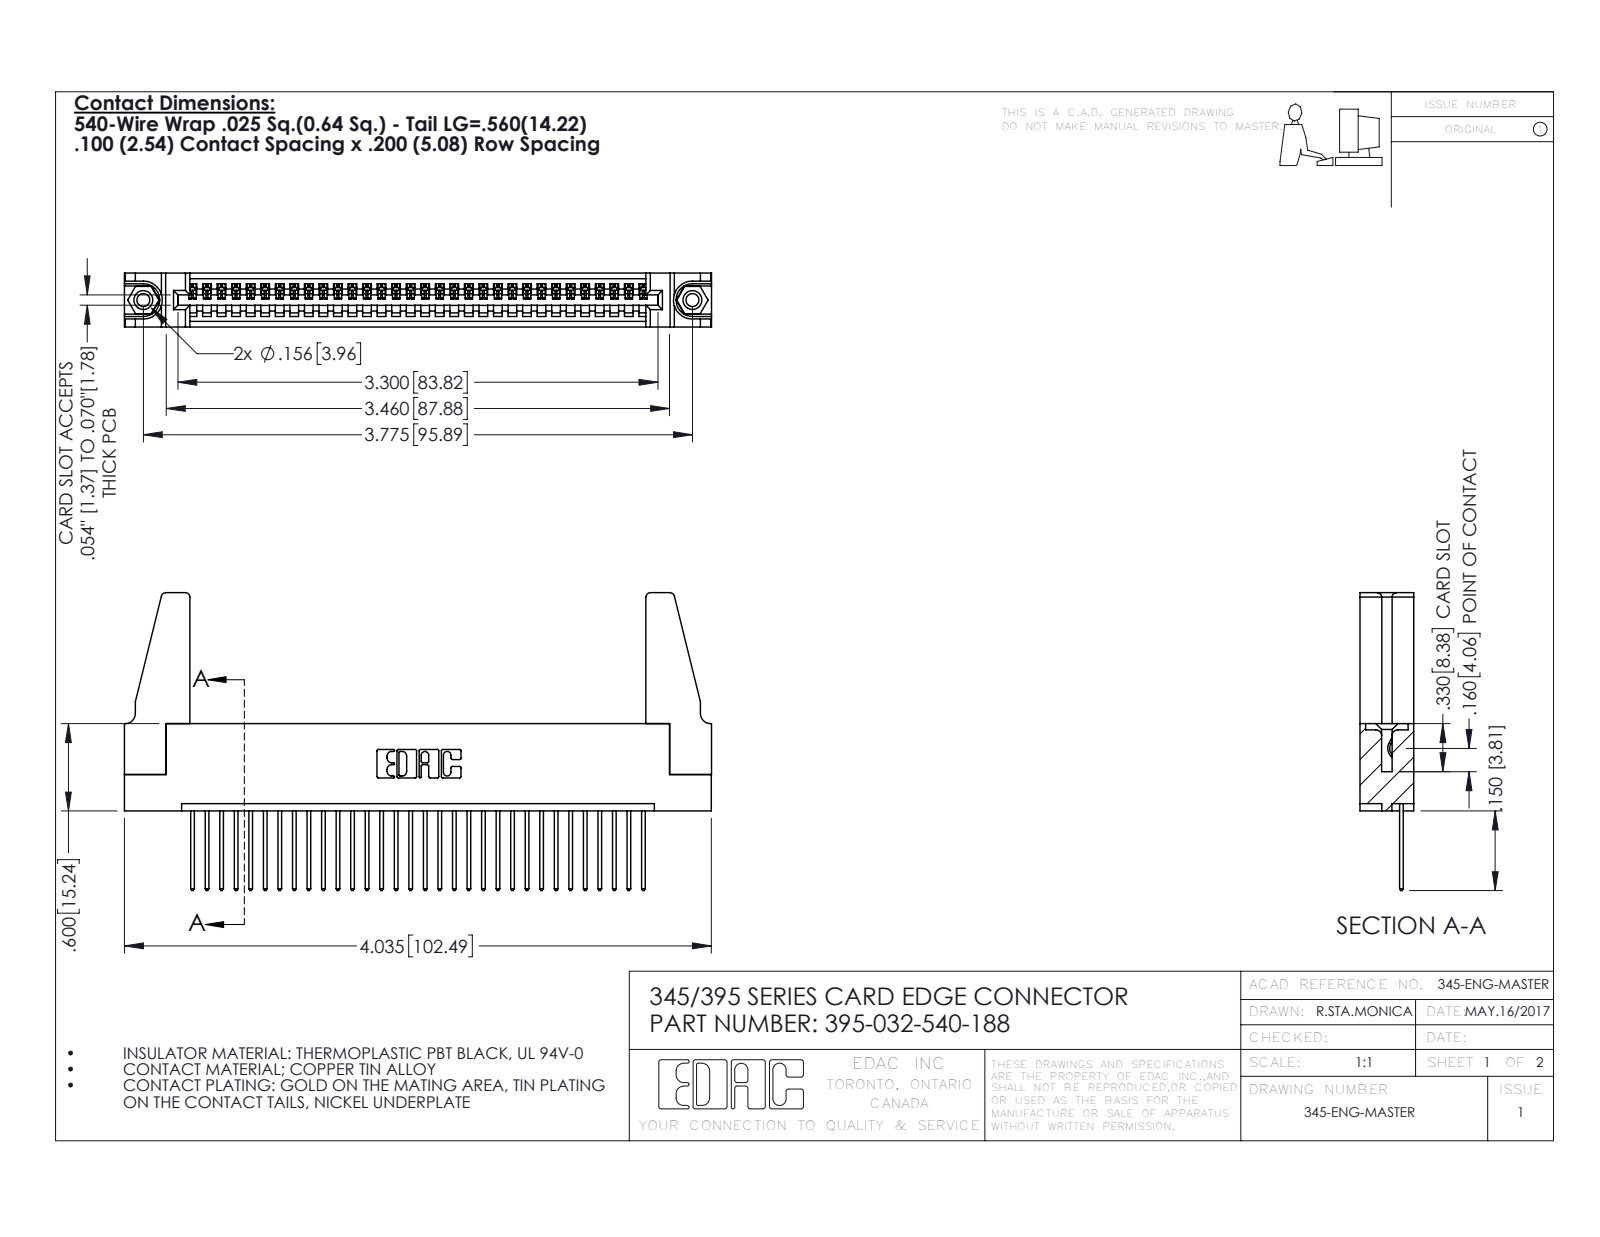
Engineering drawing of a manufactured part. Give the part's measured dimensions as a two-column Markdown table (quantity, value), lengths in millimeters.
| quantity | value |
| --- | --- |
| part name | 345-292-001_345-293-140; 345-220-078_345-220-088; 345 Part_Flush Mounting Lugs - 0.156 Dia-TH; 345-250-001_345-250-001-102 (+1 more) |
| STEP written by | SolidWorks 2016 (CONFIG_CONTROL_DESIGN) |
| units | millimeters |
| bodies | 37 solids, 2106 faces (1432 planar, 658 cylindrical, 16 other) |
| overall size | 102.5 × 52 × 9.4 |
| volume | 12 900 mm³ |
| surface area | 16 190 mm² |
| round holes (diameter × count) | 2.3 × 2, 3.2 × 2, 4 × 2, 1.6 × 1 |
| round bosses / shafts (diameter × count) | 3.9 × 2 |
| partial cylindrical surfaces (radius × count) | 0.2 × 64, 0.3 × 64, 0.3 × 22, 0.8 × 8, 0.2 × 6, 0.8 × 6, 0.7 × 3, 0.8 × 2 |
| main face-to-face distances | 1.8, 7.6, 9.4, 5.1, 2.5, 6.9, 0.6, 5.7, 3.8, 1.8 |
| hole center spacings | 6.9, 89.9, 95.9 |
